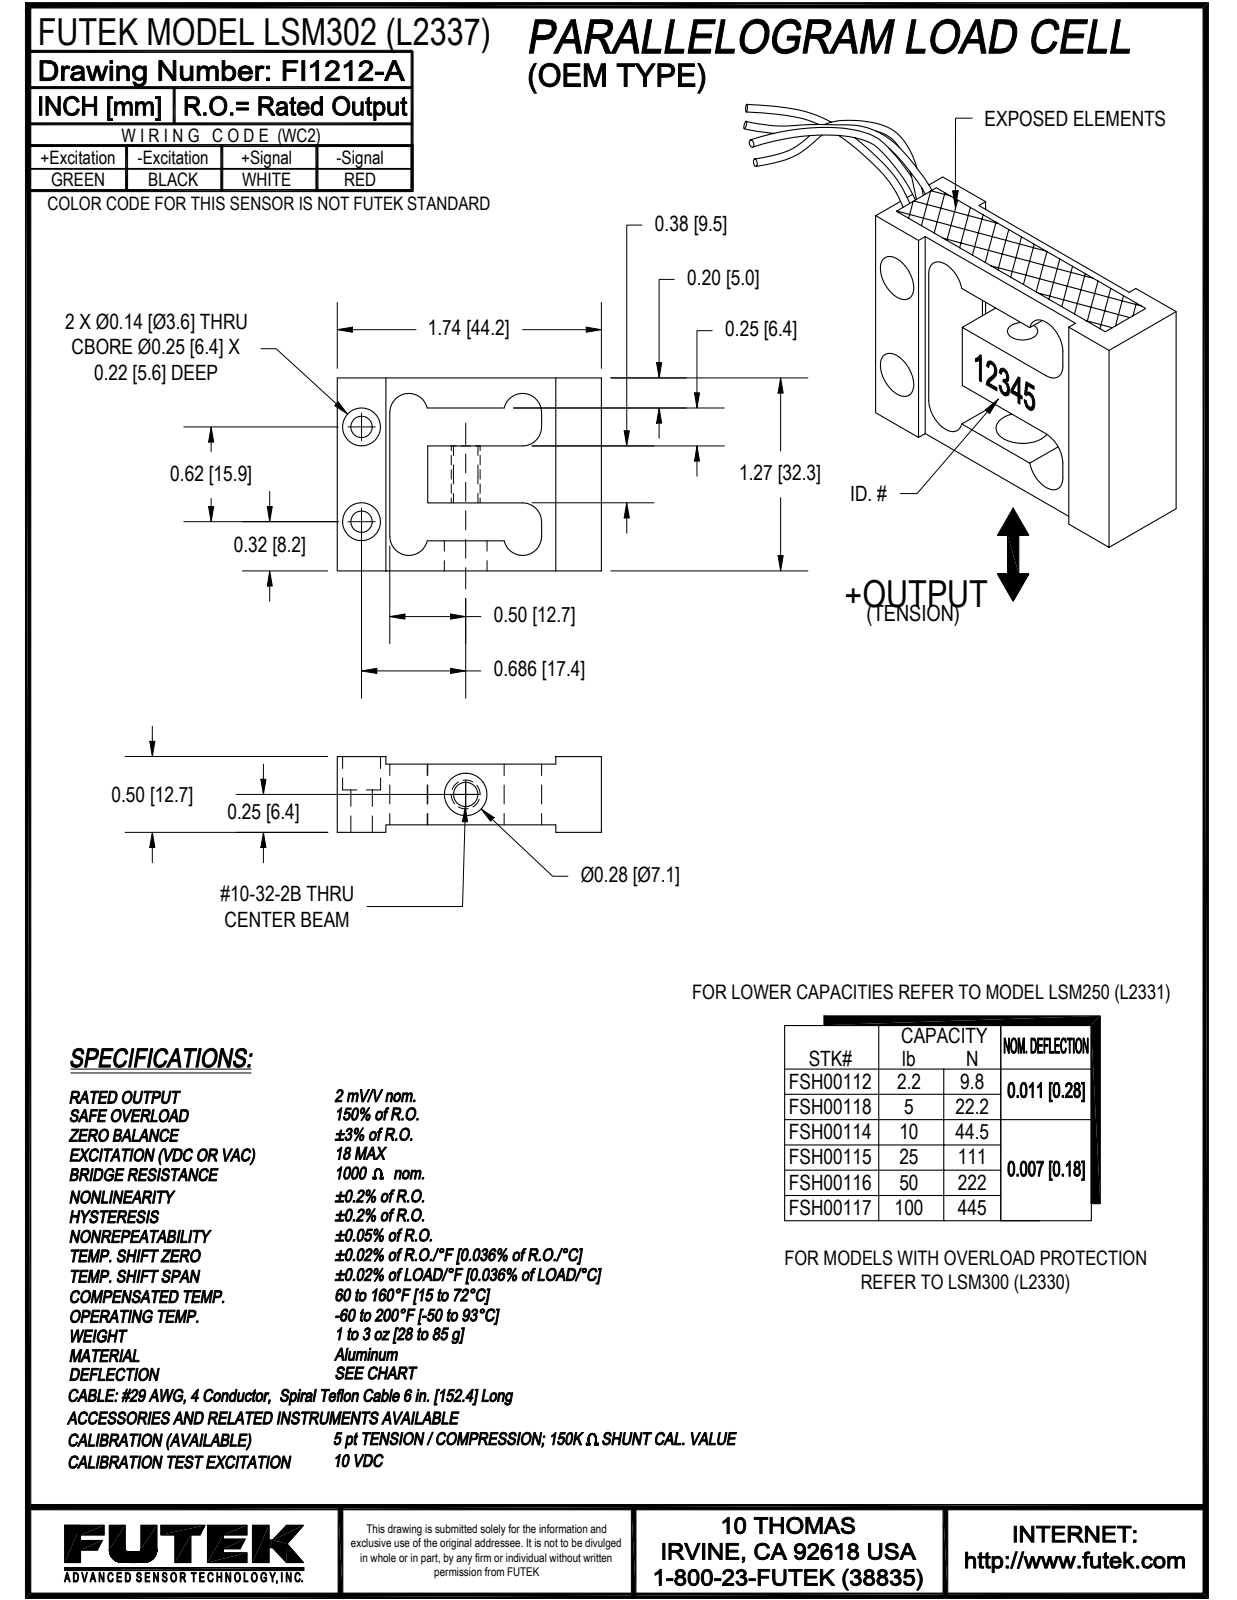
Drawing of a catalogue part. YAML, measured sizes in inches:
part_name: "FM1035; $f1666-A; NEWDWG"
step_written_by: "Mechanical Desktop 2008 (CONFIG_CONTROL_DESIGN)"
units: inches
bodies: {solids: 1, faces: 42, planar: 24, cylindrical: 18, other: 0}
overall_size: [1.74, 1.272, 0.5]
volume: 0.651
surface_area: 9.086
round_holes:
  - {diameter: 0.141, count: 2}
  - {diameter: 0.25, count: 2}
  - {diameter: 0.161, count: 1}
  - {diameter: 0.281, count: 1}
partial_cylinders:
  - {radius: 0.125, count: 6}
face_to_face_distances: [0.05, 0.45, 0.4, 1.272, 0.5, 1.74, 0.25, 0.625, 0.346, 1.394]
hole_center_spacings: [0.625]
